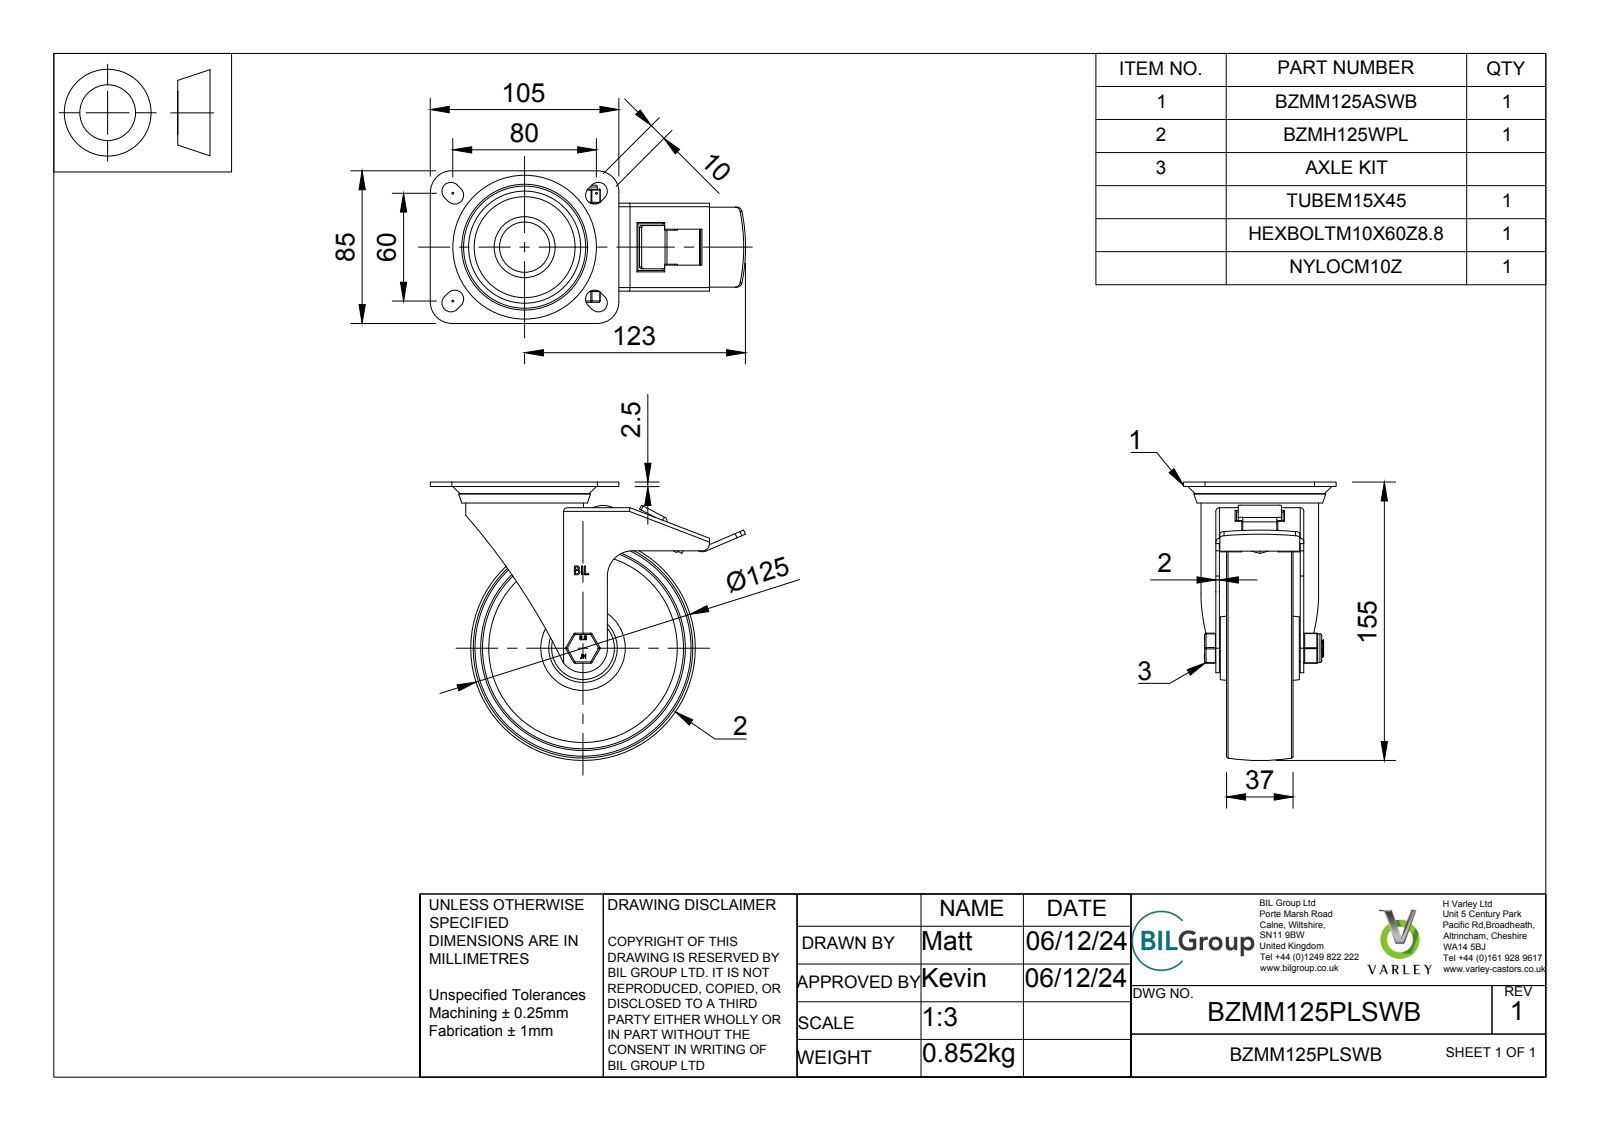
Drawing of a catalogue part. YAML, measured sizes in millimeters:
part_name: "BZMM125PLSWB v3; BZMM125ASSWB v1; ZINC PLATED, PRESSED STEEL TOP PLATE; ZINC PLATED, PRESSED STEEL FORKS (+8 more)"
step_written_by: "Autodesk Translation Framework v13.20.0.188 (AP242_MANAGED_MODEL_BASED_3D_ENGINEERING_MIM_LF)"
units: millimeters
bodies: {solids: 13, faces: 615, planar: 315, cylindrical: 199, other: 101}
overall_size: [175.5, 155, 85]
volume: 273156
surface_area: 137097
round_holes:
  - {diameter: 6, count: 2}
  - {diameter: 10, count: 1}
  - {diameter: 10.2, count: 1}
  - {diameter: 12, count: 1}
  - {diameter: 15.2, count: 1}
  - {diameter: 28, count: 1}
  - {diameter: 40, count: 1}
  - {diameter: 61.5, count: 1}
  - {diameter: 112, count: 1}
round_bosses_or_shafts:
  - {diameter: 65.5, count: 1}
  - {diameter: 34, count: 1}
  - {diameter: 16, count: 1}
  - {diameter: 15.5, count: 1}
  - {diameter: 14.95, count: 1}
  - {diameter: 9.85, count: 1}
  - {diameter: 8.14, count: 1}
partial_cylinders:
  - {radius: 0.5, count: 18}
  - {radius: 0.75, count: 16}
  - {radius: 1.5, count: 12}
  - {radius: 5, count: 9}
  - {radius: 1, count: 8}
  - {radius: 2, count: 6}
  - {radius: 3, count: 4}
  - {radius: 12, count: 4}
face_to_face_distances: [2, 6, 21.5, 4, 27.5, 2.5, 47, 19.5, 25.5, 5]
hole_center_spacings: [43.75]
